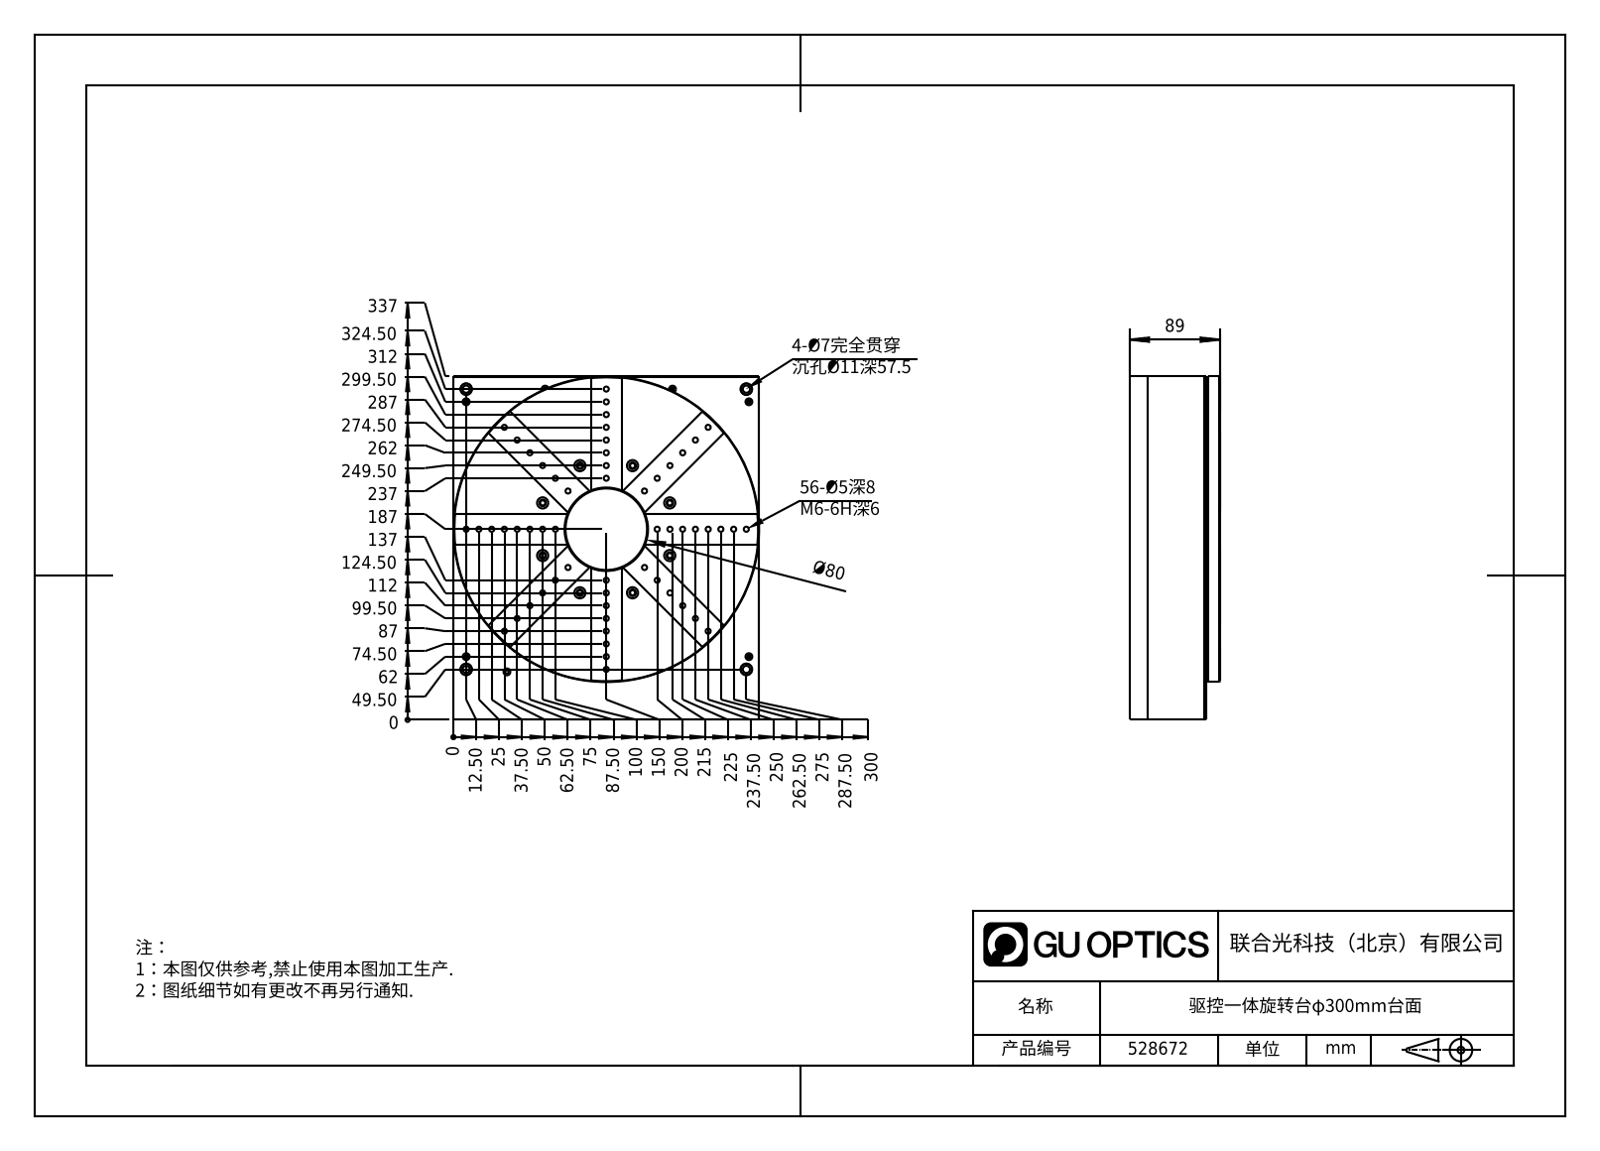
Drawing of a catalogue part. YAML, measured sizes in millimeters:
part_name: "528672"
step_written_by: "SolidWorks 2020 (CONFIG_CONTROL_DESIGN)"
units: millimeters
bodies: {solids: 22, faces: 2864, planar: 367, cylindrical: 2059, other: 438}
overall_size: [337, 300, 89]
volume: 5268000
surface_area: 965412
round_holes:
  - {diameter: 5, count: 81}
  - {diameter: 11, count: 23}
  - {diameter: 5.5, count: 20}
  - {diameter: 6.6, count: 19}
  - {diameter: 3.3, count: 15}
  - {diameter: 2.5, count: 12}
  - {diameter: 10, count: 11}
  - {diameter: 3.4, count: 10}
  - {diameter: 4.2, count: 10}
  - {diameter: 4.5, count: 10}
  - {diameter: 8, count: 10}
  - {diameter: 9.5, count: 10}
round_bosses_or_shafts:
  - {diameter: 15.6, count: 2}
  - {diameter: 300, count: 1}
  - {diameter: 175, count: 1}
  - {diameter: 170, count: 1}
  - {diameter: 165, count: 1}
  - {diameter: 163.5, count: 1}
  - {diameter: 118, count: 1}
  - {diameter: 38.2, count: 1}
partial_cylinders:
  - {radius: 3.3, count: 8}
  - {radius: 5.5, count: 8}
  - {radius: 2, count: 6}
  - {radius: 16, count: 2}
  - {radius: 1, count: 1}
face_to_face_distances: [25, 73, 55, 18, 75.5, 3.5, 58.5, 13, 1, 76.5]
hole_center_spacings: [33.33, 47.14, 125, 57.01, 48.5, 78.47, 29.97, 29.98]
